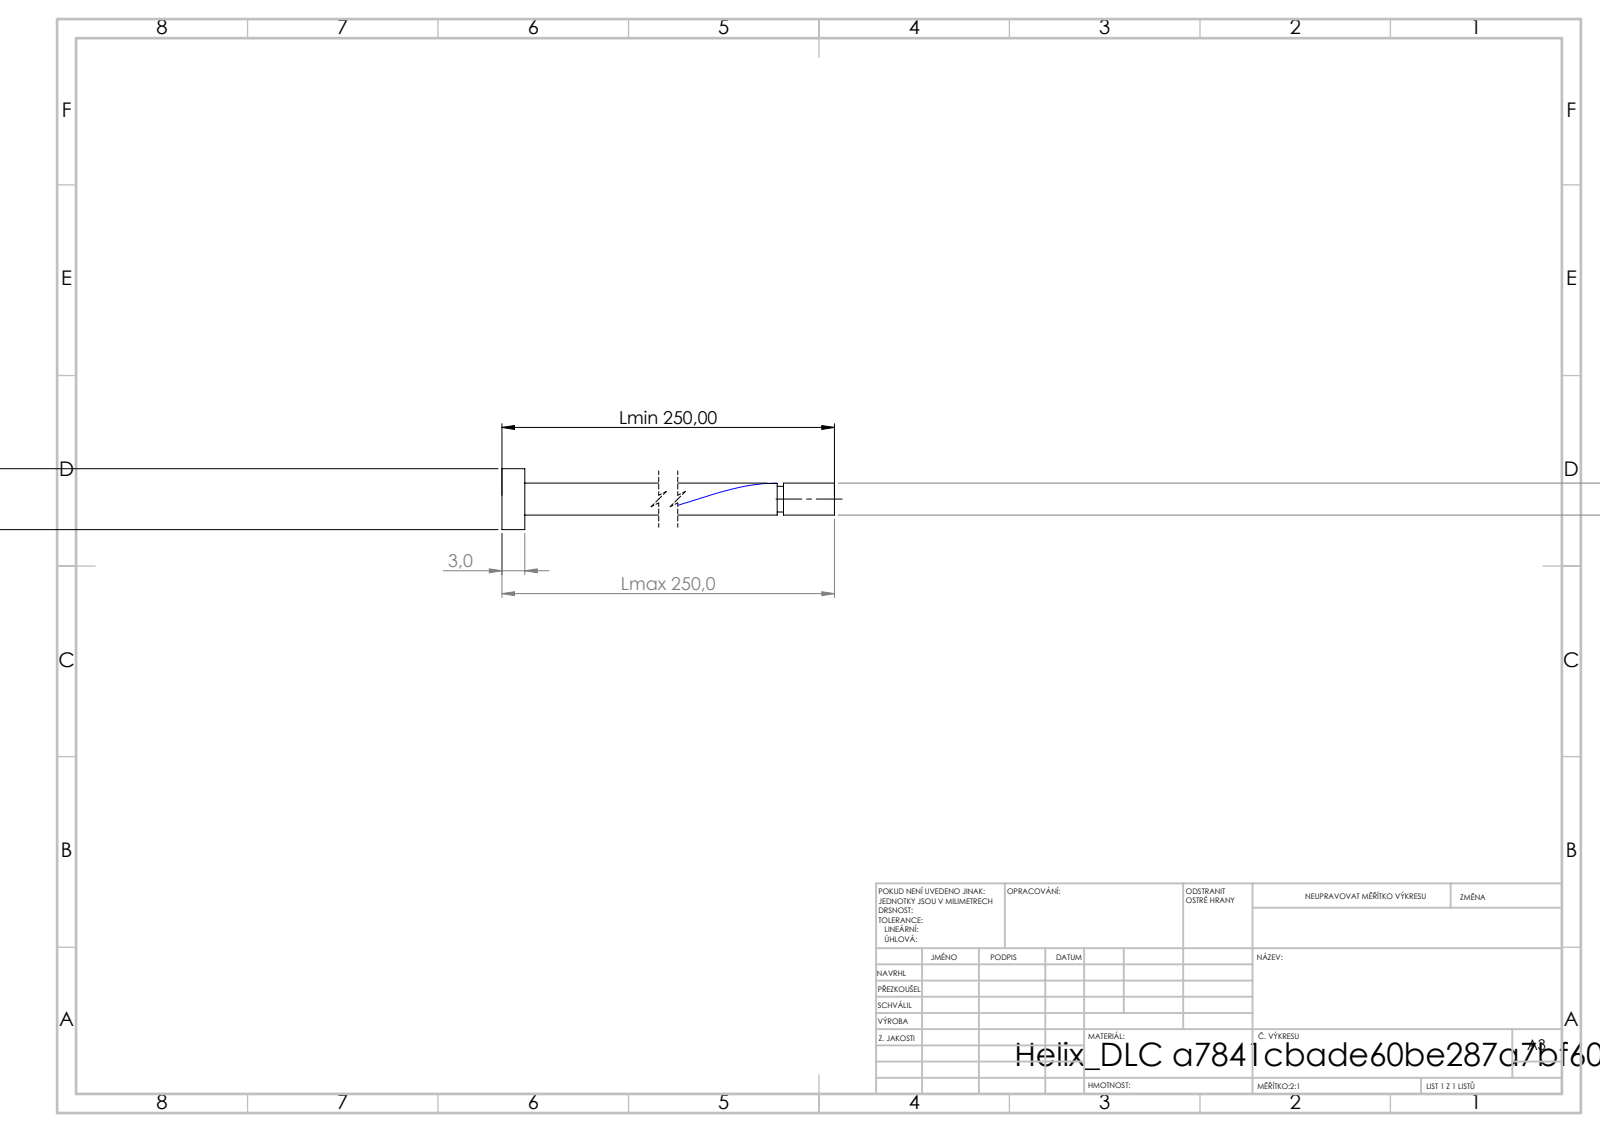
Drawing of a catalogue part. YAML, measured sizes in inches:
step_written_by: "SolidWorks 2019 (CONFIG_CONTROL_DESIGN)"
units: inches
bodies: {solids: 1, faces: 16, planar: 6, cylindrical: 9, other: 1}
overall_size: [9.843, 0.315, 0.315]
volume: 0.263
surface_area: 7.124
round_bosses_or_shafts:
  - {diameter: 0.315, count: 1}
  - {diameter: 0.165, count: 1}
  - {diameter: 0.132, count: 1}
face_to_face_distances: [0.118, 9.843, 9.724, 9.58, 9.461, 0.263, 9.546, 9.428, 0.033, 0.296]
